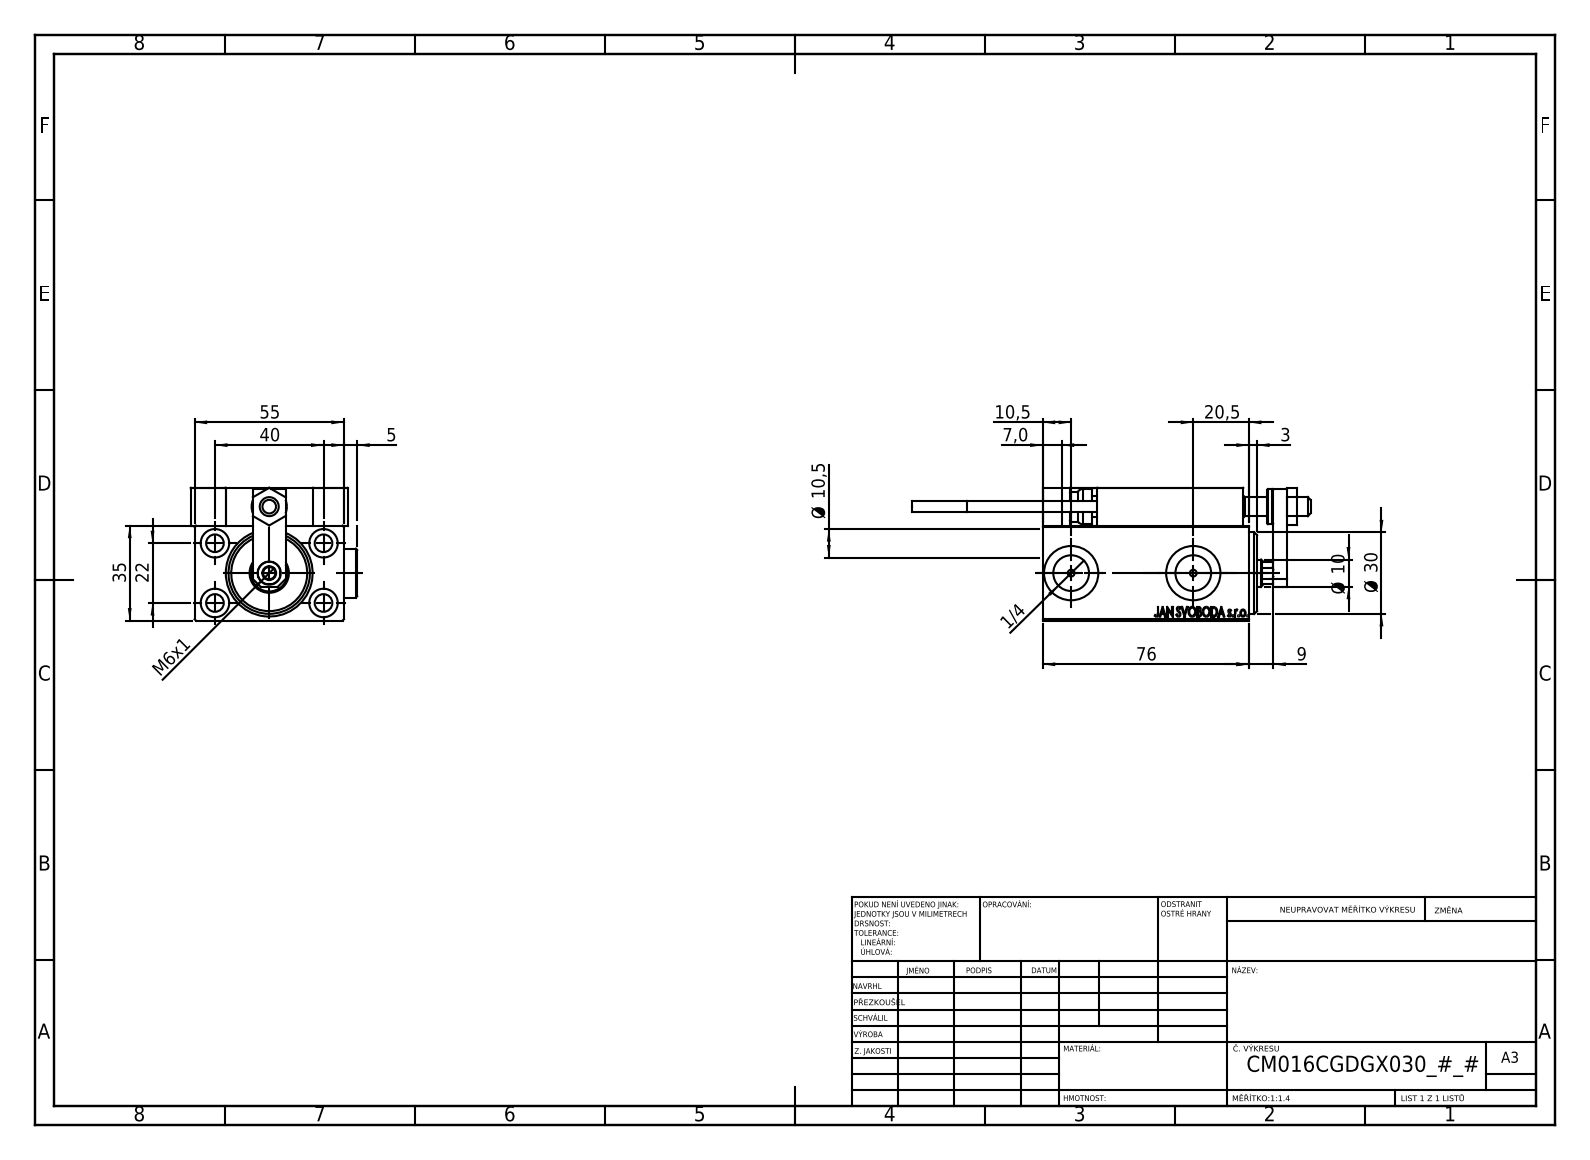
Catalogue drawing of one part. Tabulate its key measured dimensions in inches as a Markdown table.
| quantity | value |
| --- | --- |
| part name | V450CM_C_Body; NUT_D12; SWITCH DIM B,W; V450CM_C_VCP (+7 more) |
| STEP written by | SolidWorks 2019 (CONFIG_CONTROL_DESIGN) |
| units | inches |
| bodies | 25 solids, 1339 faces (595 planar, 206 cylindrical, 538 other) |
| overall size | 5.776 × 2.417 × 1.929 |
| volume | 10.31 in³ |
| surface area | 93.07 in² |
| round holes (diameter × count) | 0.315 × 5, 0.126 × 4, 0.157 × 4, 0.256 × 4, 0.413 × 4, 0.098 × 2, 0.197 × 2, 0.518 × 2, 0.787 × 2, 0.177 × 1, 0.276 × 1, 0.335 × 1 |
| round bosses / shafts (diameter × count) | 0.709 × 2, 0.197 × 2, 0.15 × 2, 0.512 × 1, 0.433 × 1 |
| partial cylindrical surfaces (radius × count) | 0.012 × 30, 0.118 × 2, 0.177 × 1 |
| main face-to-face distances | 1.378, 0.197, 0.551, 1.929, 0.394, 0.276, 0.118, 2.165, 0.512, 0.059 |
| hole center spacings | 0.899, 0.448, 0.787, 0.866, 0.95, 1.105, 1.165, 1.169 |
